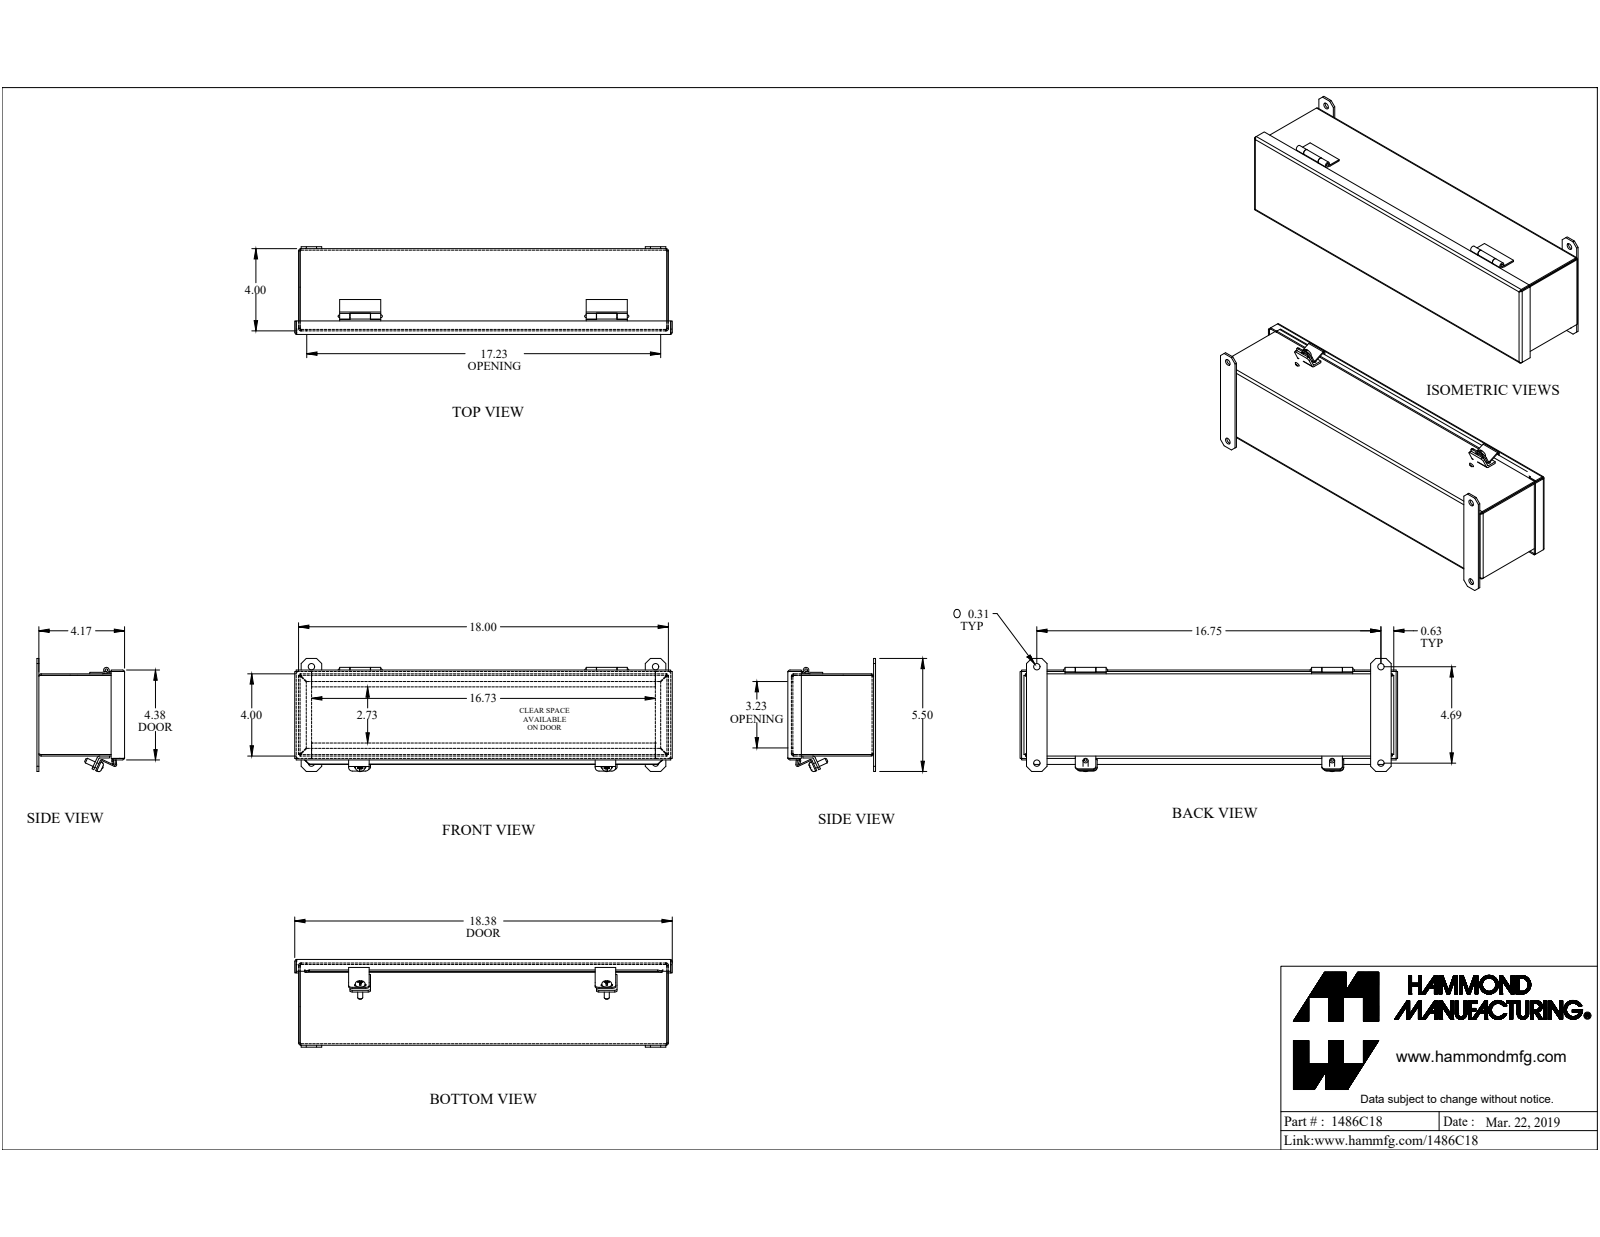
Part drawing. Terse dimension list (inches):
name: 1486C18
written by: SolidWorks 2019 (CONFIG_CONTROL_DESIGN)
unit: in
bodies: 22 solids, 488 faces (325 planar, 112 cylindrical, 51 other)
size: 18.375 × 5.506 × 4.903
volume: 34.12 in³; area: 871.8 in²
holes: 4× ⌀0.313, 2× ⌀0.213, 1× ⌀0.125
bosses: 3× ⌀0.48, 3× ⌀0.246, 1× ⌀0.275
rounds: 13× R0.036, 13× R0.108, 12× R0.25, 10× R0.188, 6× R0.01, 6× R0.141, 4× R0.029, 4× R0.086
face distances: 0.072, 3.928, 4.1, 4, 3.856, 4.172, 4.028, 0.187, 0.259, 3.913
hole spacings: 4.688, 16.75, 17.394, 12
